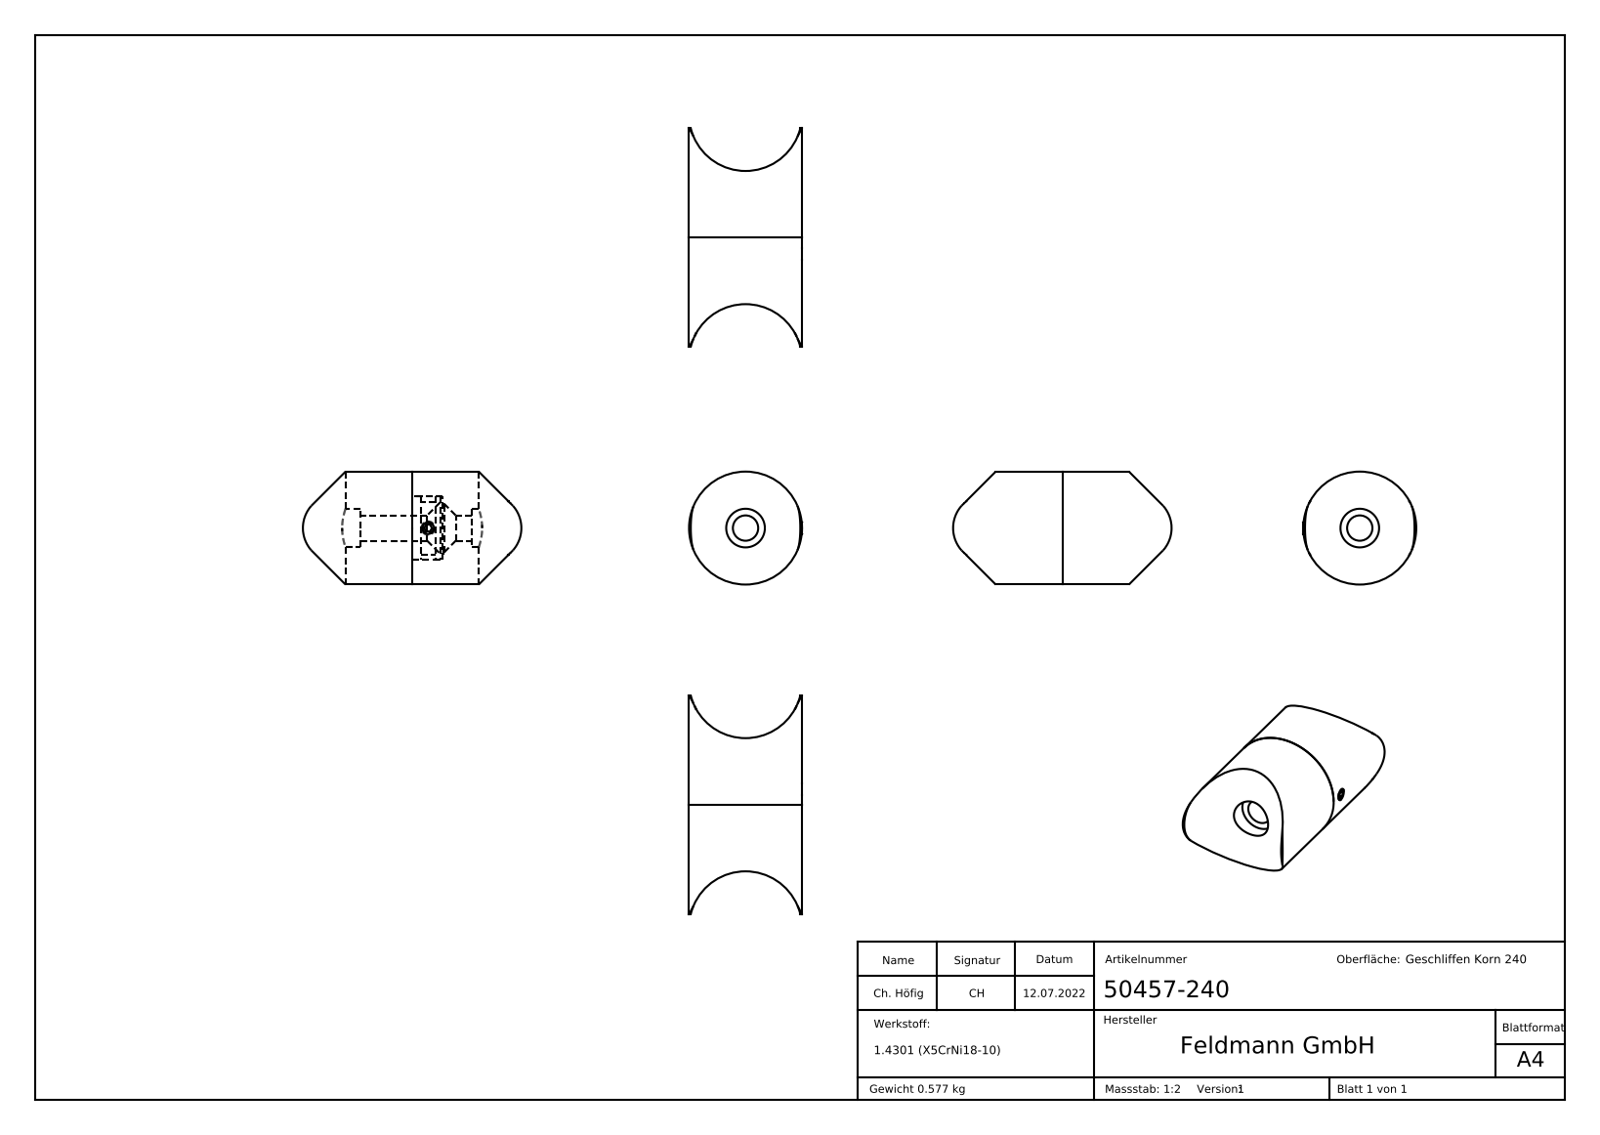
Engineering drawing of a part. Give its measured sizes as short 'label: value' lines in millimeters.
name: 50457-240 DIN913 M5x10_DIN913 M5x10; 50457-240; 50457-240 Teil1_50457-240 Teil1; 50457-240 Teil2_50457-240 Teil2
written by: SolidWorks 2018 (CONFIG_CONTROL_DESIGN)
unit: mm
bodies: 3 solids, 268 faces (153 planar, 23 cylindrical, 92 other)
size: 82 × 42.4 × 42.4
volume: 73 089 mm³; area: 18 312 mm²
holes: 1× ⌀4.2, 1× ⌀9.5, 1× ⌀14.5, 1× ⌀18.25, 1× ⌀24
bosses: 1× ⌀42.4, 1× ⌀23.75, 1× ⌀19.75, 1× ⌀5
rounds: 2× R12.63, 2× R21.2
face distances: 11.5, 1, 10.5, 2.7, 1.7, 8.8, 8.2, 7.2, 5.5, 3.3
